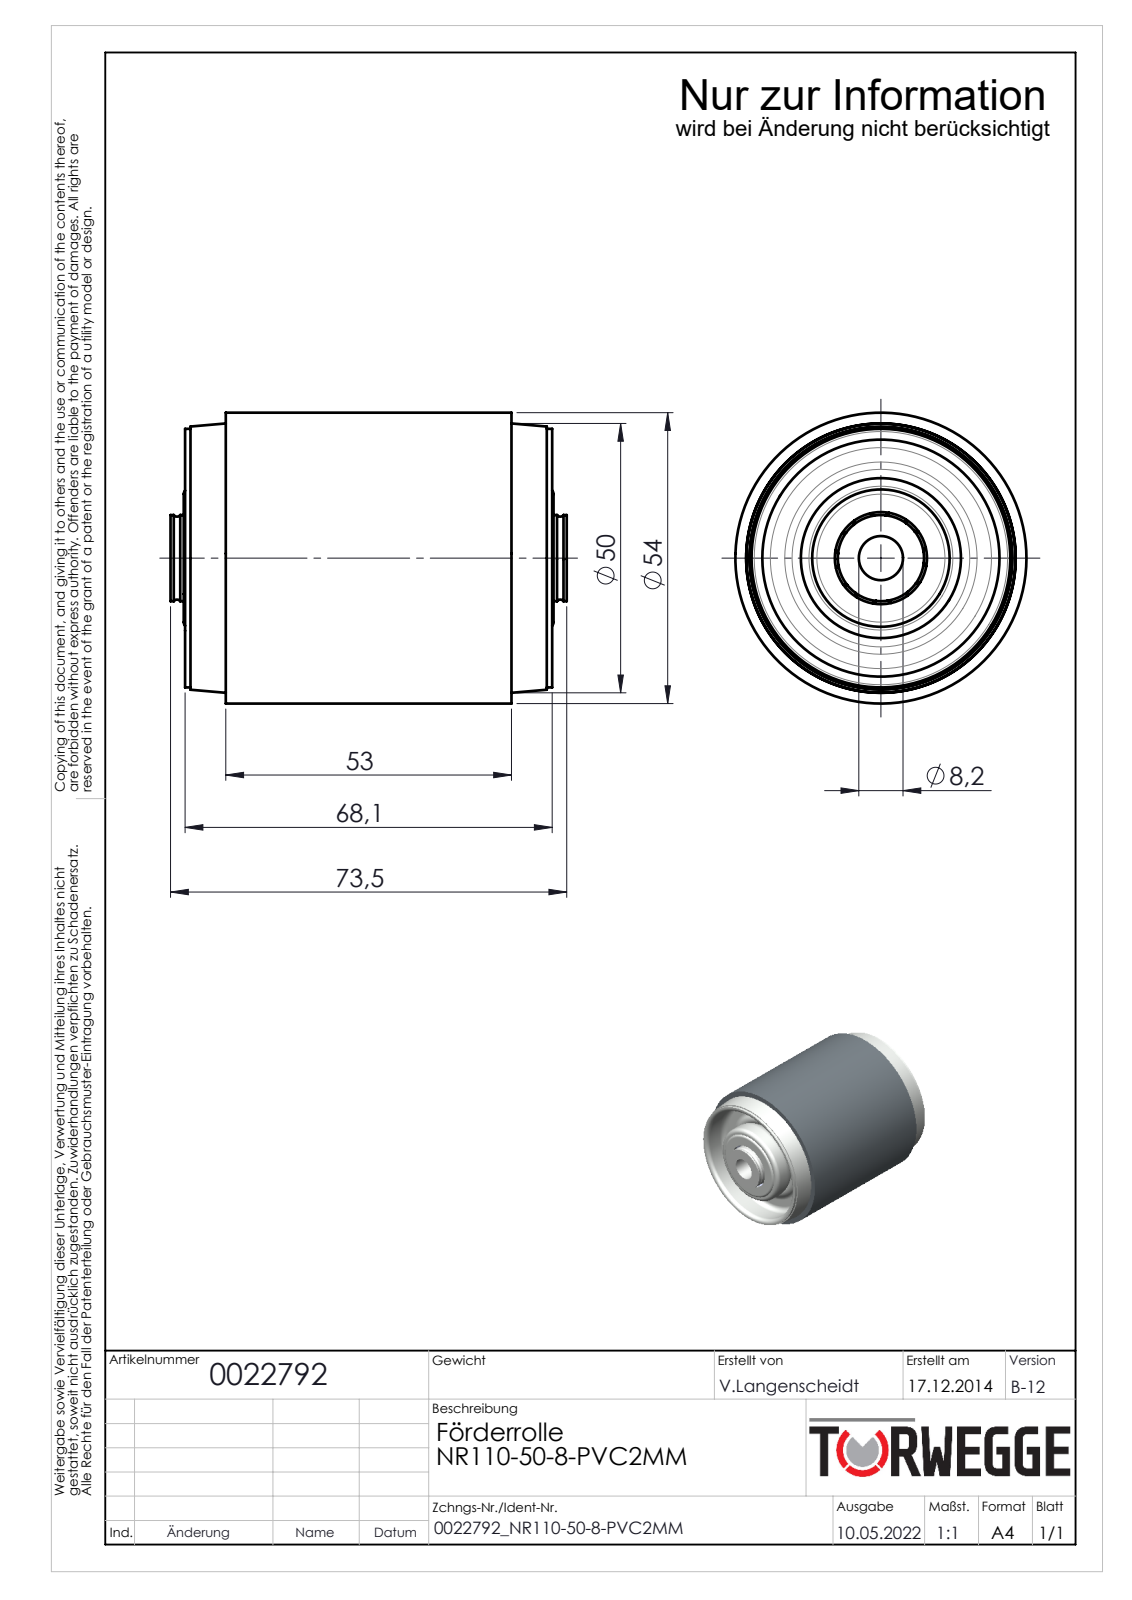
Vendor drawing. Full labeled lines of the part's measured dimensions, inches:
Part name (STEP PRODUCT): 0022792
STEP written by: SolidWorks 2020 (AUTOMOTIVE_DESIGN)
Units: inches
Bodies: 26 solids, 438 faces (82 planar, 76 cylindrical, 280 other)
Overall size (bounding box): 2.894 × 2.126 × 2.126
Volume: 2.86 in³ · Surface area: 96.93 in²
Round holes (diameter × count): ⌀0.323 ×1, ⌀0.673 ×1, ⌀0.728 ×1, ⌀0.756 ×1, ⌀1.091 ×1, ⌀1.85 ×1, ⌀1.969 ×1
Round bosses / shafts (diameter × count): ⌀2.126 ×1, ⌀1.89 ×1, ⌀1.169 ×1, ⌀1.079 ×1, ⌀1.075 ×1, ⌀0.913 ×1, ⌀0.63 ×1
Partial cylindrical surfaces — rounded edges, fillets, slot ends (radius × count): R0.348 ×1
Main face-to-face distances: 0.039, 0.384, 2.278, 0.374, 2.268, 0.116, 1.97, 0.077, 2.01, 1.894
